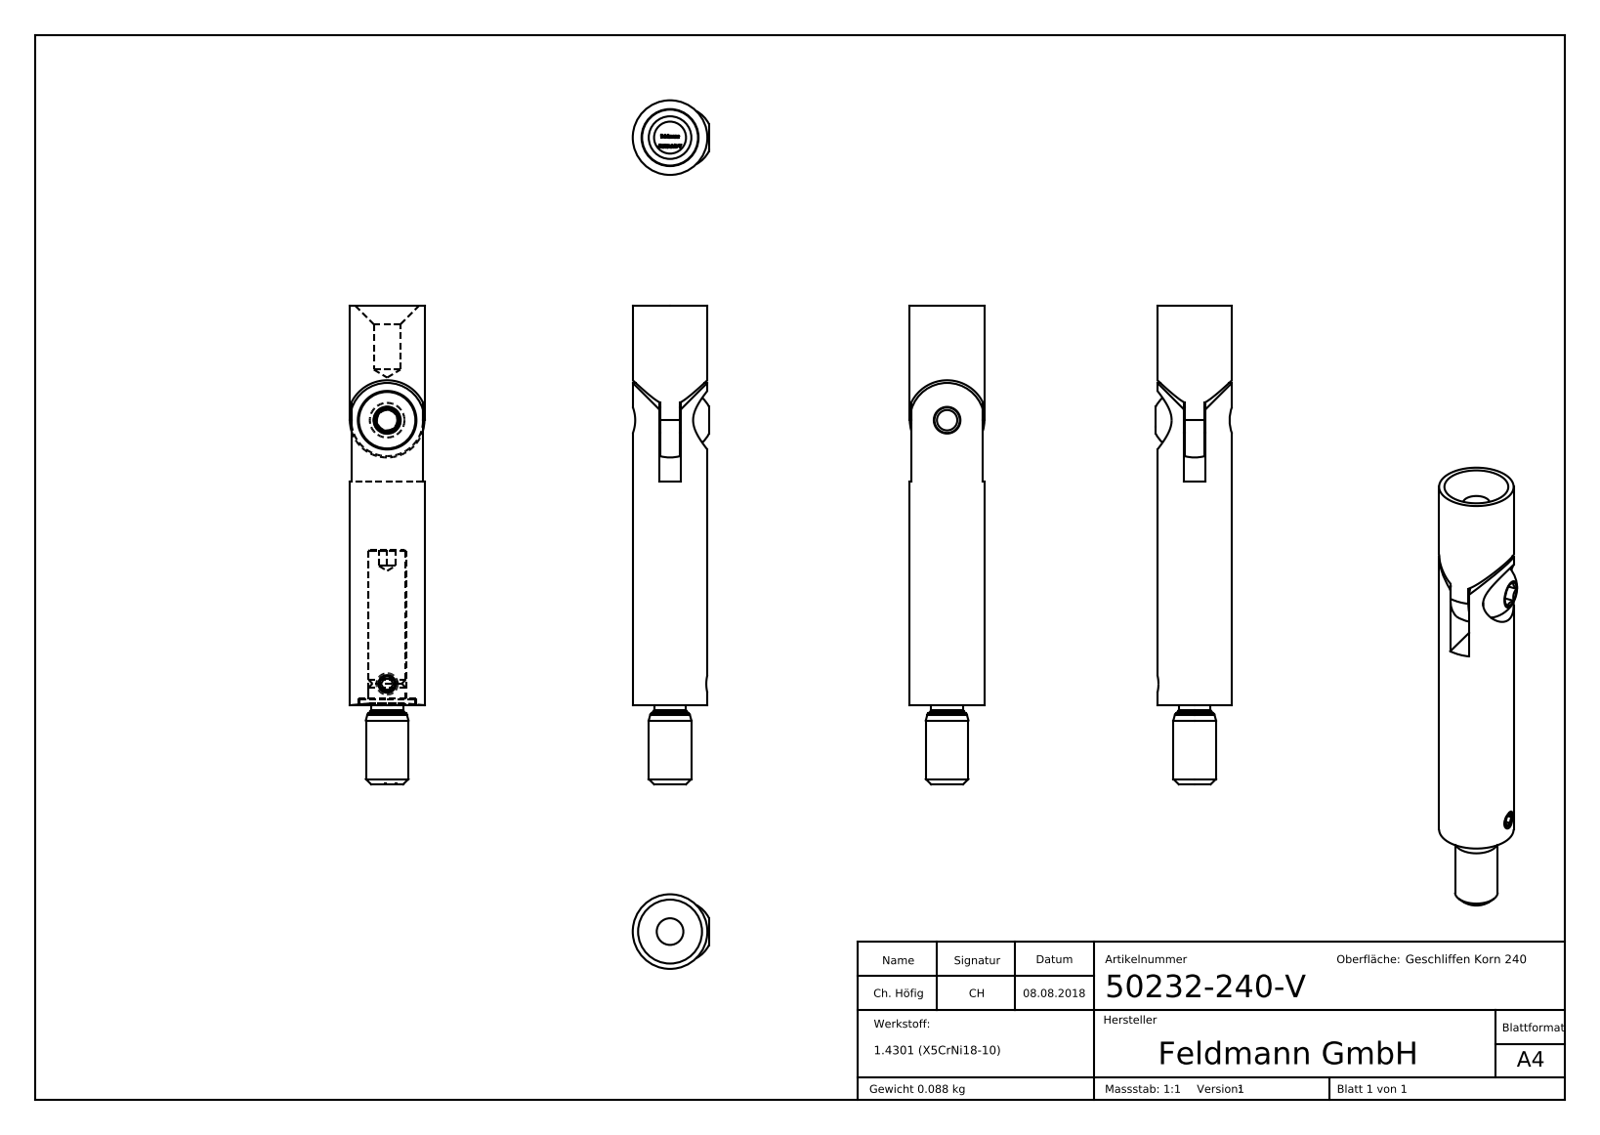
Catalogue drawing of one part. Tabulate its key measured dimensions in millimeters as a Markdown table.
| quantity | value |
| --- | --- |
| part name | 50232-240-V Teil2_50232-240-V Teil2; 50232-240-V Teil3_50232-240-V Teil3; DIN 914 M4x4_DIN 914 M4x4; ISO 7380 M6x8_ISO 7380 M6x10 (+2 more) |
| STEP written by | SolidWorks 2015 (CONFIG_CONTROL_DESIGN) |
| units | millimeters |
| bodies | 5 solids, 370 faces (176 planar, 40 cylindrical, 154 other) |
| overall size | 89.85 × 14.3 × 14 |
| volume | 11 159 mm³ |
| surface area | 7 265 mm² |
| round holes (diameter × count) | 5 × 2, 3.3 × 1, 6.5 × 1, 7.1 × 1, 10.7 × 1, 11 × 1 |
| round bosses / shafts (diameter × count) | 14 × 1, 10.6 × 1, 10.5 × 1, 8 × 1, 7 × 1, 6 × 1, 4.77 × 1, 4 × 1 |
| partial cylindrical surfaces (radius × count) | 7 × 1, 7.5 × 1 |
| main face-to-face distances | 3.87, 4, 2, 6, 2.13, 3.74, 5.87, 40.8, 40.85, 73.85 |
| hole center spacings | 49.5 |
